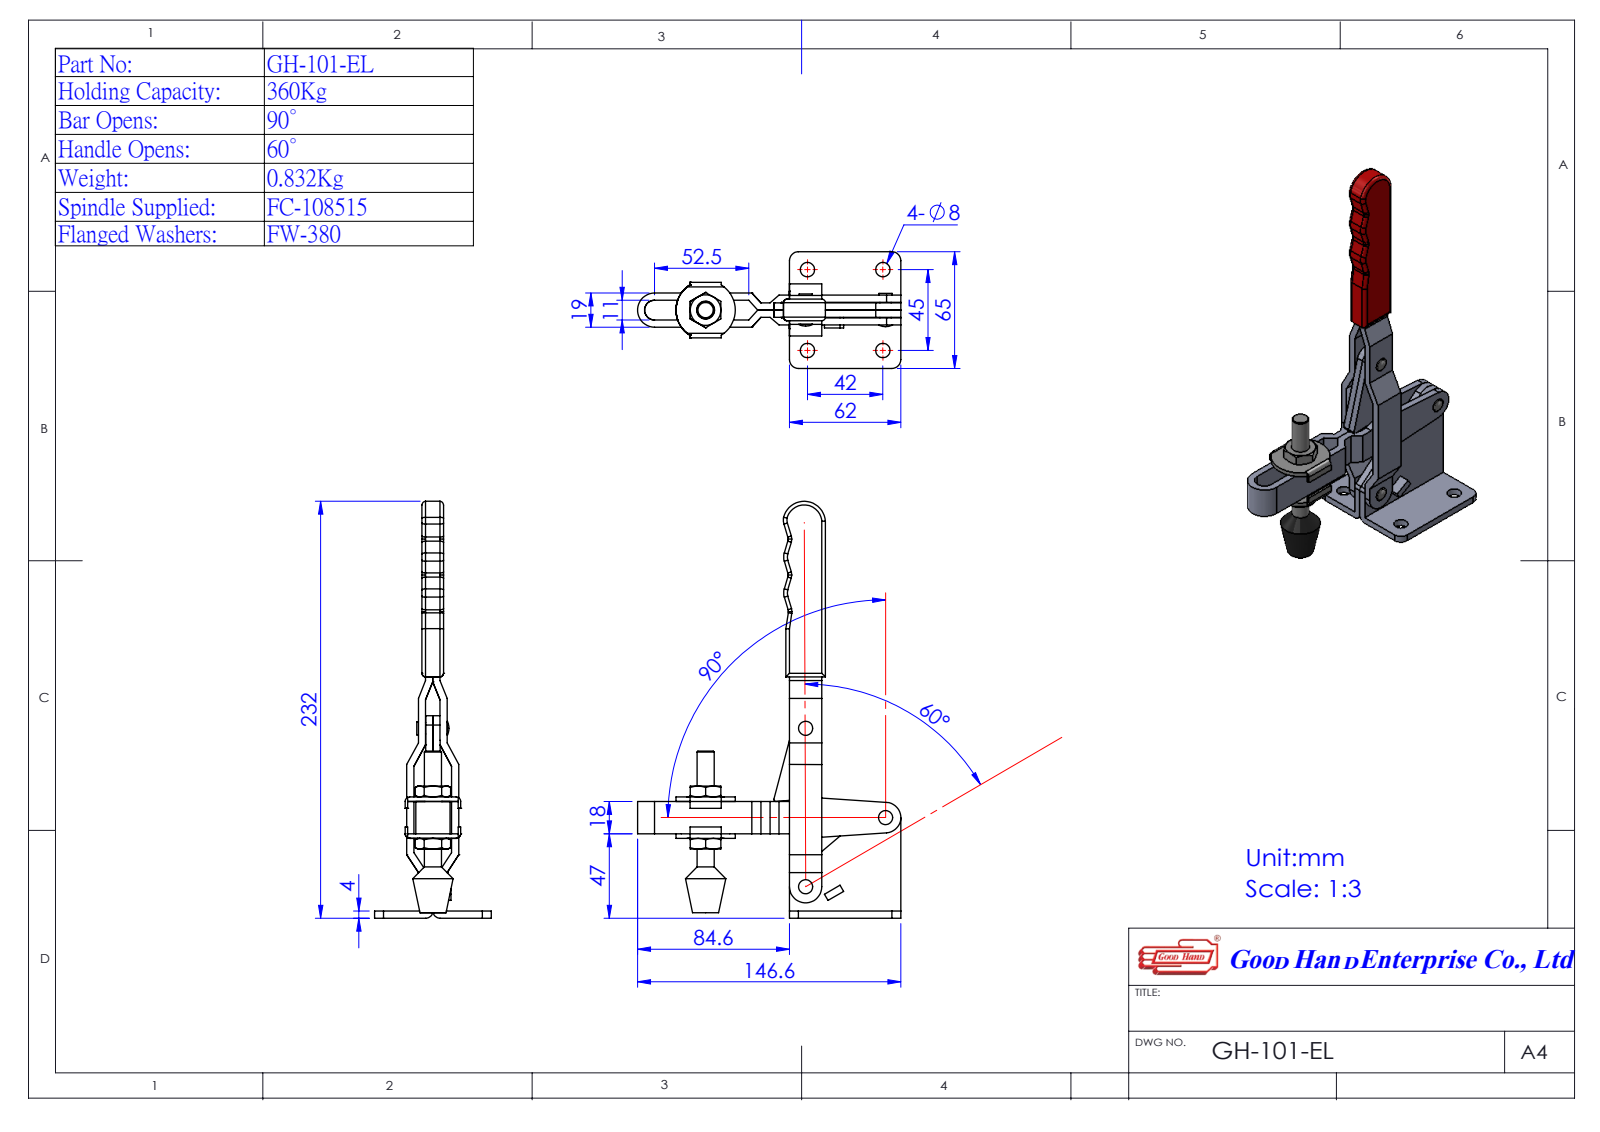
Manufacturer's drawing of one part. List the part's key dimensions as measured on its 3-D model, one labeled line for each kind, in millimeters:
Part name (STEP PRODUCT): Group5^GH-101-EL(簡化); Group2^GH-101-EL(簡化); Group3^GH-101-EL(簡化); GH-101-EL(簡化) (+2 more)
STEP written by: SolidWorks 2016 (AUTOMOTIVE_DESIGN)
Units: millimetres
Bodies: 5 solids, 267 faces (139 planar, 90 cylindrical, 38 other)
Overall size (bounding box): 232 × 146.6 × 65
Volume: 129 109 mm³ · Surface area: 59 458 mm²
Round holes (diameter × count): ⌀4.5 ×4, ⌀8 ×4
Round bosses / shafts (diameter × count): ⌀7.3 ×4, ⌀9.53 ×1
Partial cylindrical surfaces — rounded edges, fillets, slot ends (radius × count): R2.54 ×4, R5 ×4, R4 ×3, R8 ×3, R1 ×2, R7 ×2, R12 ×2, R3 ×1
Main face-to-face distances: 4, 2, 8, 20, 10, 1.2, 13.8, 12.3, 5, 6.2
Hole centre spacings: 42, 45, 61.55, 38.49, 44.2, 49.71, 58.84, 66.7
